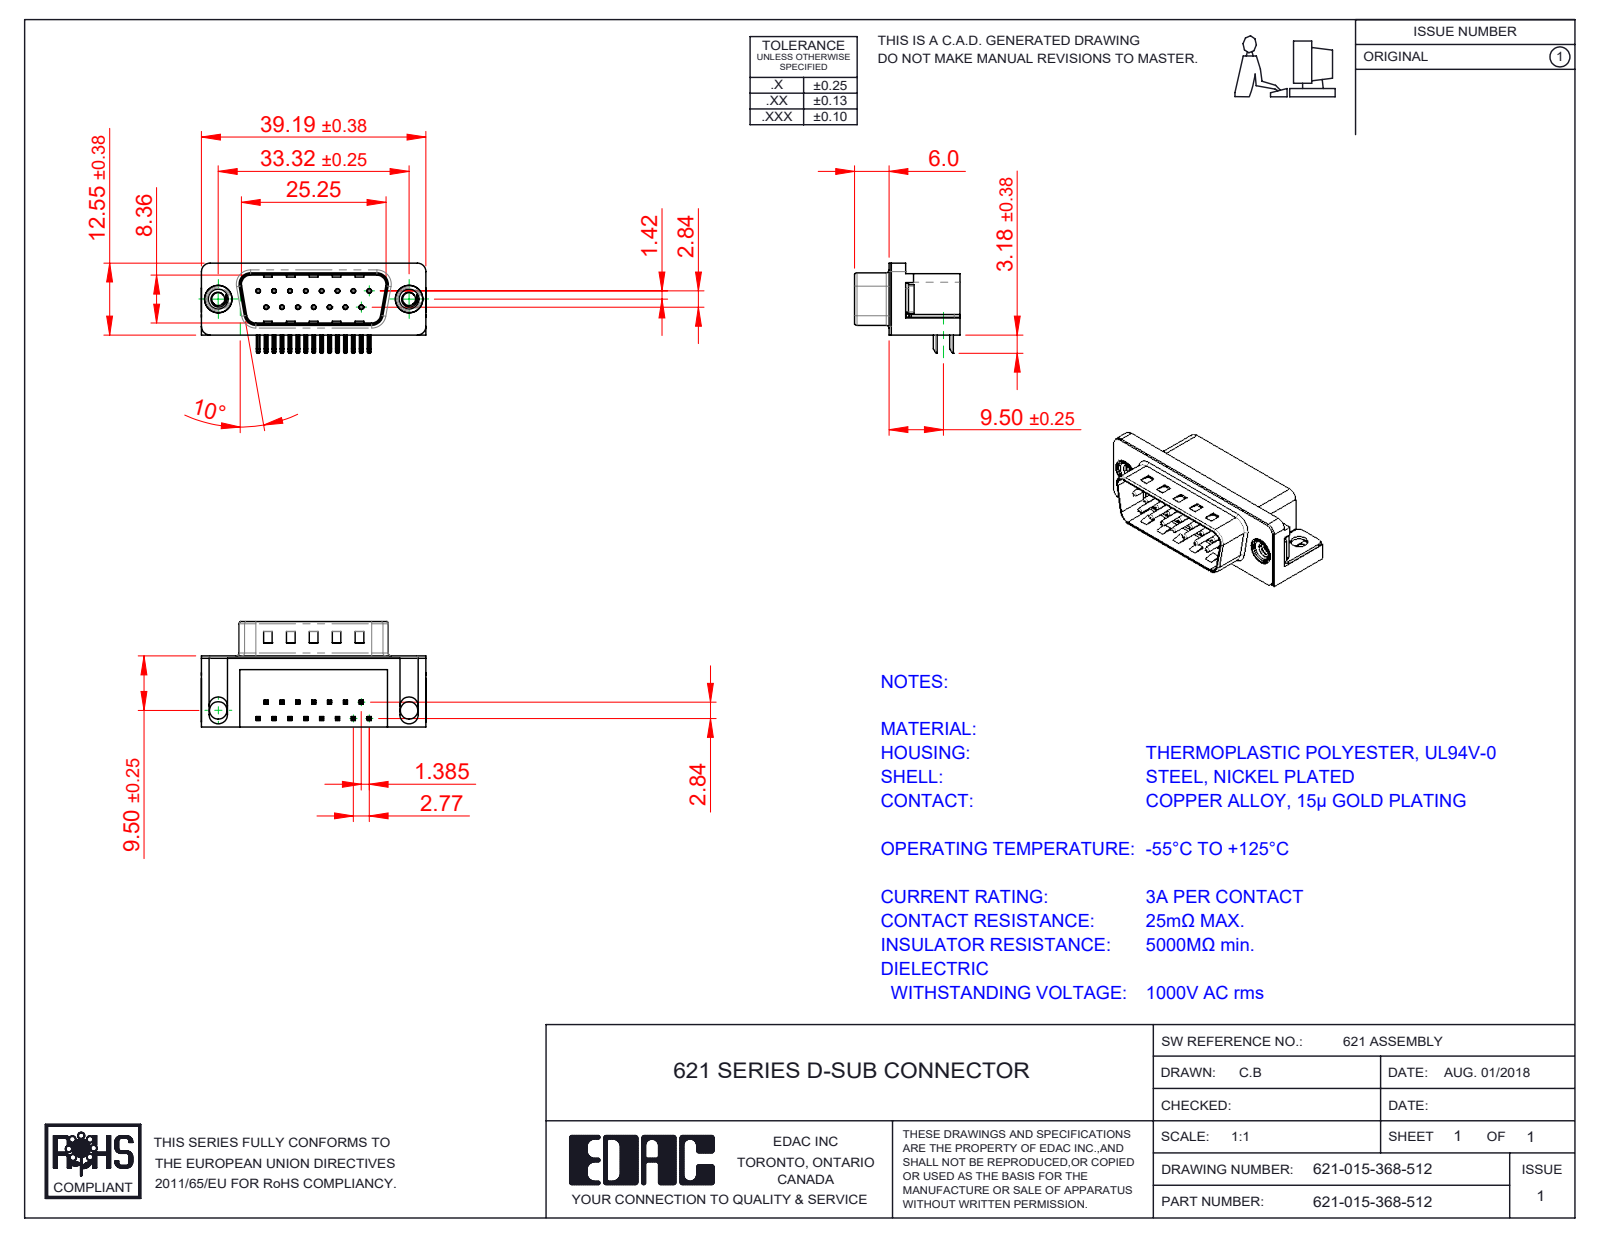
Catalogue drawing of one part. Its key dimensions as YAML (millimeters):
part_name: "621 Contact Top; 621-015-368-512; 621 Shell_15 Socket; 621 Housing_15 Socket (+3 more)"
step_written_by: "SolidWorks 2016 (CONFIG_CONTROL_DESIGN)"
units: millimeters
bodies: {solids: 21, faces: 1475, planar: 891, cylindrical: 445, other: 139}
overall_size: [39.22, 18.4, 15.73]
volume: 4414
surface_area: 5637
round_holes:
  - {diameter: 0.35, count: 15}
  - {diameter: 0.8, count: 15}
  - {diameter: 2.26, count: 2}
  - {diameter: 3.05, count: 2}
  - {diameter: 4, count: 2}
  - {diameter: 4.8, count: 2}
  - {diameter: 5, count: 2}
round_bosses_or_shafts:
  - {diameter: 0.75, count: 15}
  - {diameter: 4.9, count: 2}
  - {diameter: 4.75, count: 2}
  - {diameter: 3.9, count: 2}
partial_cylinders:
  - {radius: 0.25, count: 68}
  - {radius: 0.12, count: 30}
  - {radius: 1, count: 16}
  - {radius: 0.5, count: 9}
  - {radius: 1.6, count: 8}
  - {radius: 1.5, count: 6}
  - {radius: 0.9, count: 4}
  - {radius: 2, count: 4}
face_to_face_distances: [0.4, 12, 10.35, 2.1, 10.46, 12.4, 1.7, 10.86, 8.76, 2.9]
hole_center_spacings: [3.16, 2.77, 5.54, 8.31, 11.08, 5.03, 5.04, 7.48]
